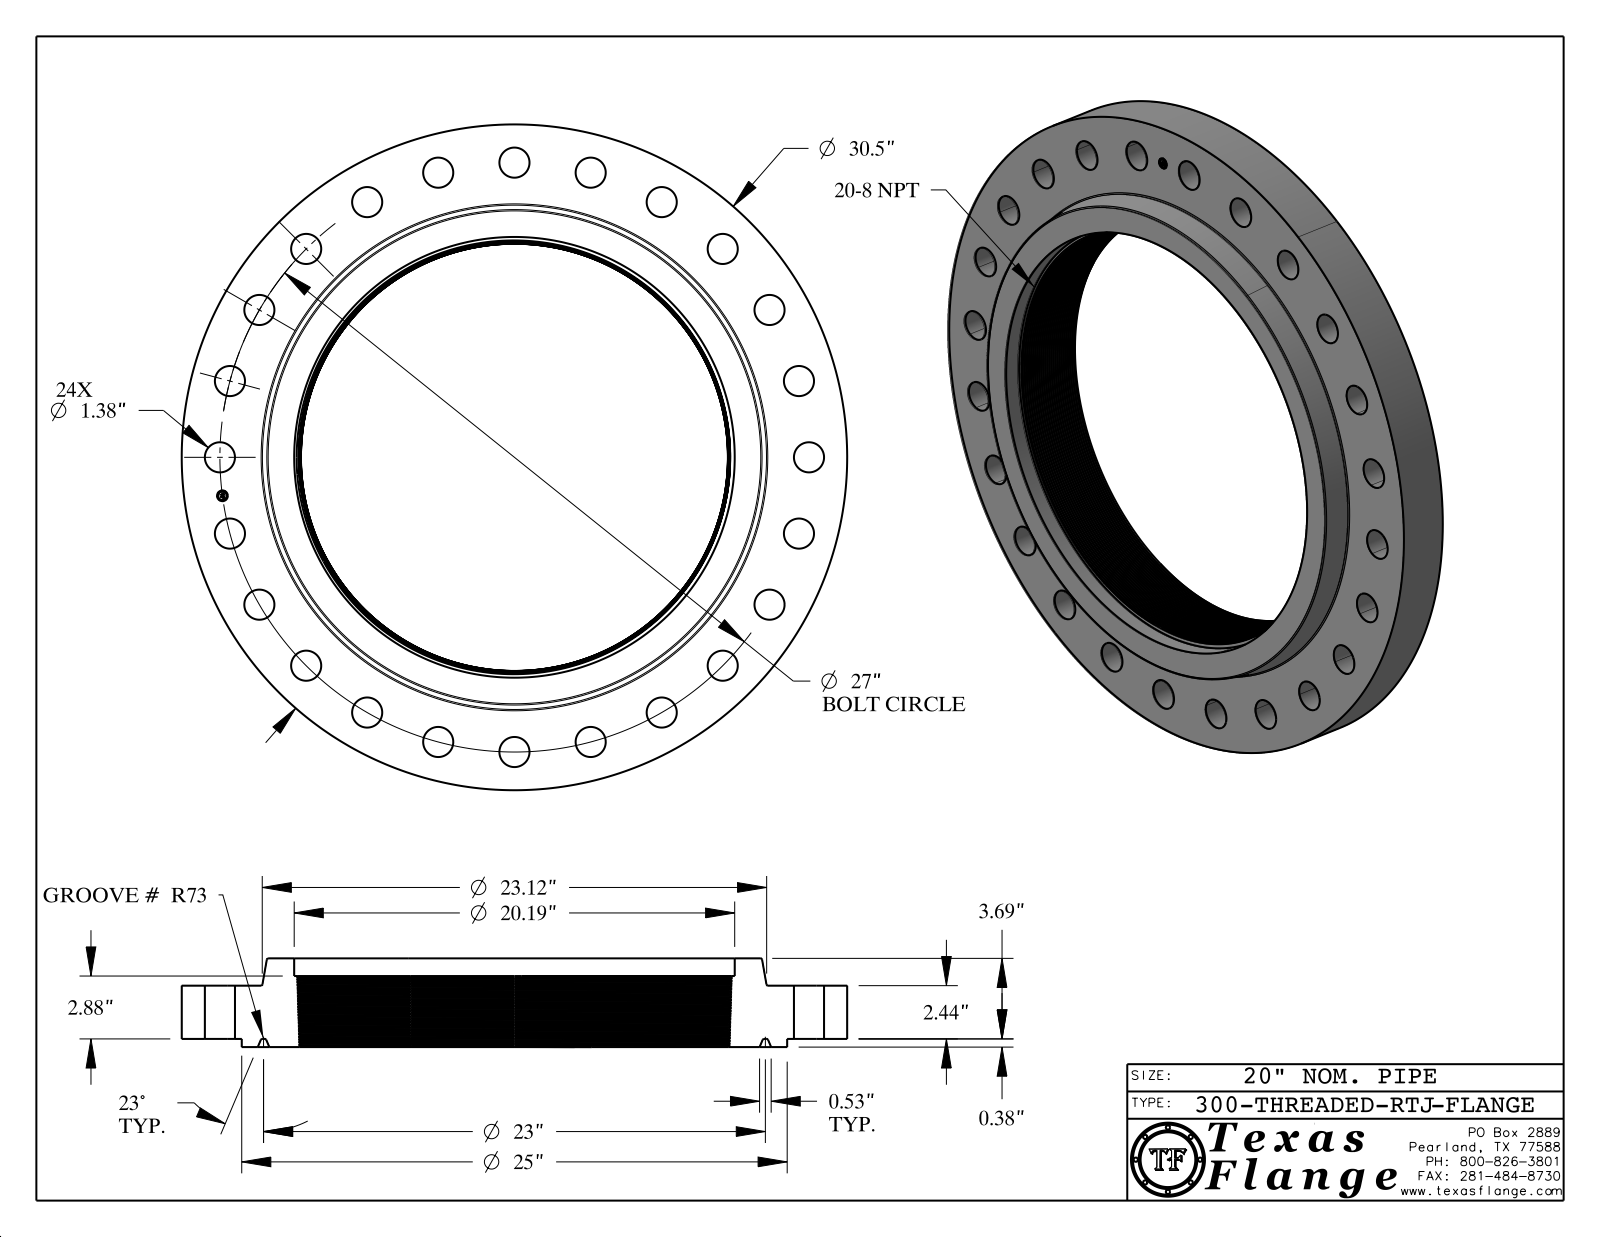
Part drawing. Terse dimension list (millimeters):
name: 300-THREADED-RTJ
written by: CATIA V5 STEP AP214 (AUTOMOTIVE_DESIGN)
unit: mm
bodies: 1 solid, 728 faces (372 planar, 74 cylindrical, 282 other)
size: 774.7 × 774.7 × 103.3
volume: 18 450 000 mm³; area: 1 181 000 mm²
holes: 24× ⌀35.1, 1× ⌀12.6, 1× ⌀512.8
bosses: 8× ⌀0.8, 1× ⌀774.7, 1× ⌀635, 1× ⌀9.9
face distances: 62, 9.5, 71.5, 103.3, 93.7, 31.8, 82.7, 73.2, 11.2, 20.6
hole spacings: 342.9, 89.5, 177.5, 262.5, 417.5, 633.6, 679.9, 544.1
